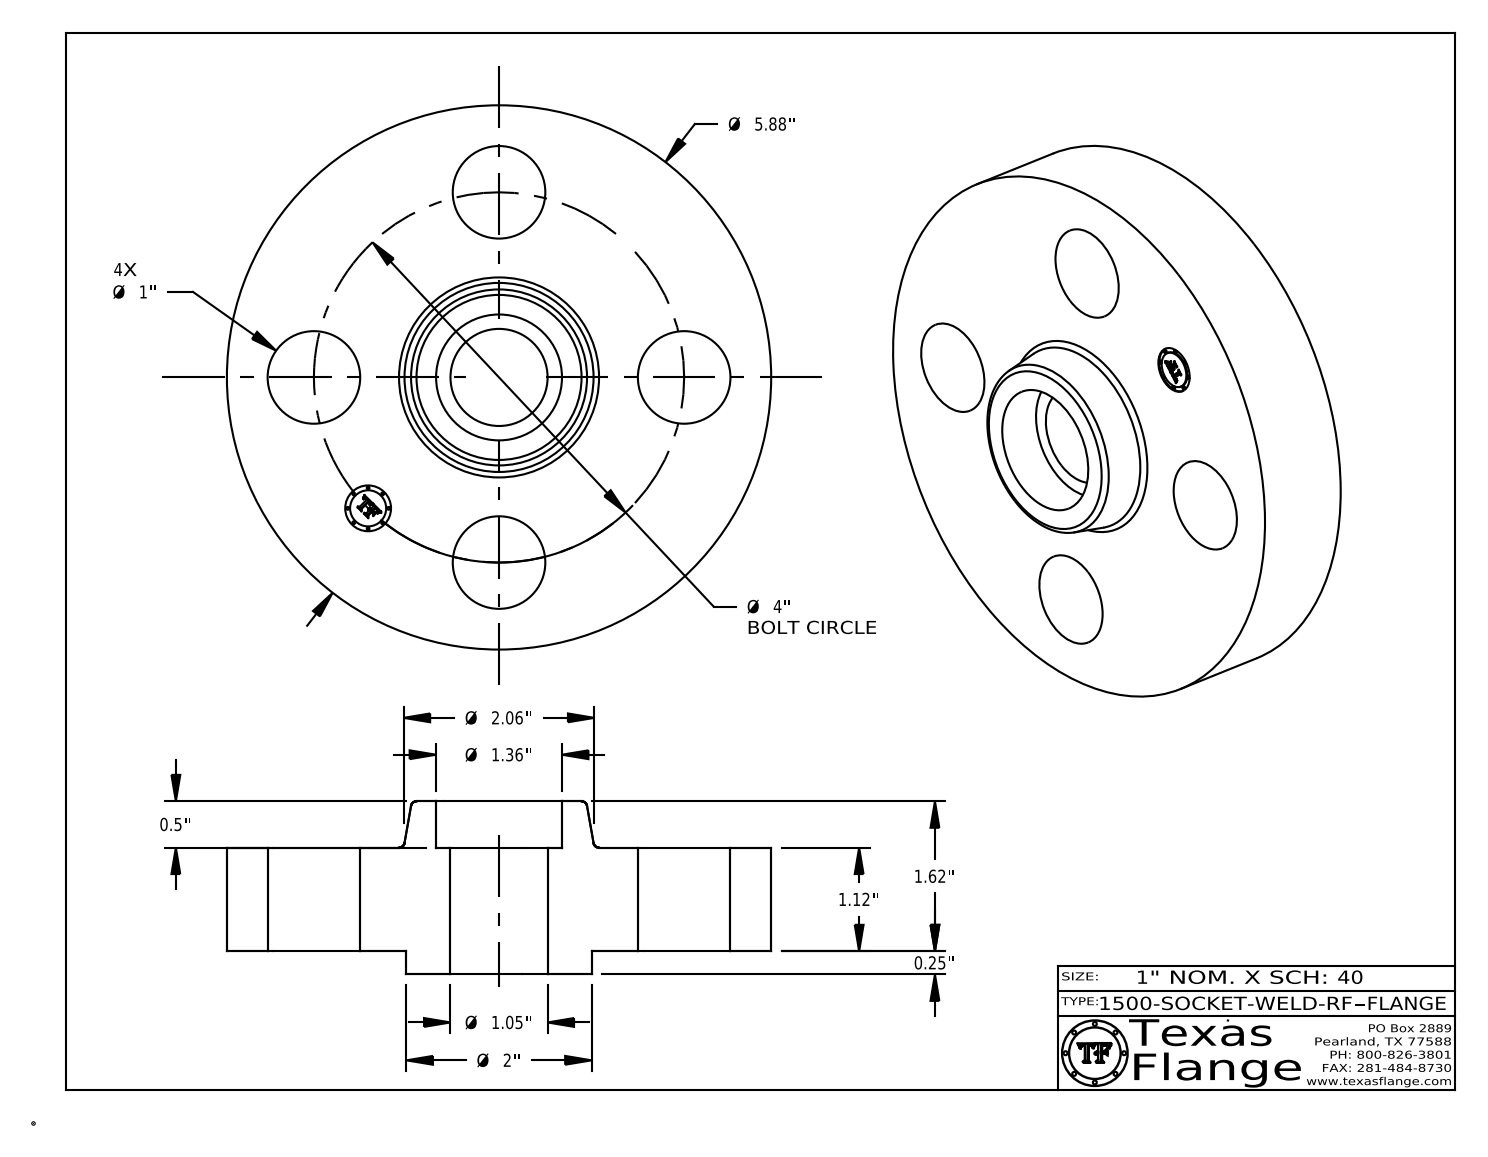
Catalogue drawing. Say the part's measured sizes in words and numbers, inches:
The part is named "1500-SOCKET-WELD-RF". Its 3-D file was written by "CATIA V5 STEP AP214 (AUTOMOTIVE_DESIGN)". It is 1 solid with 412 faces: 370 planar, 36 cylindrical and 6 other. Overall it measures 5.88 by 5.88 by 1.87 inches. Its volume is 27.3 cubic inches and its surface area 91.77 square inches. Round holes: 4 of diameter 1, 1 of diameter 0.495, 1 of diameter 1.049, 1 of diameter 1.36. Round bosses or shafts: 8 of diameter 0.03, 1 of diameter 5.88, 1 of diameter 2, 1 of diameter 0.39. The main face-to-face distances are 1.12, 0.25, 1.37, 1.87, 1.62, 0.5, 0.015, 1.355, 1.105, 0.515. The hole center spacings are 2, 2.828, 1.531, 3.695, 4.
